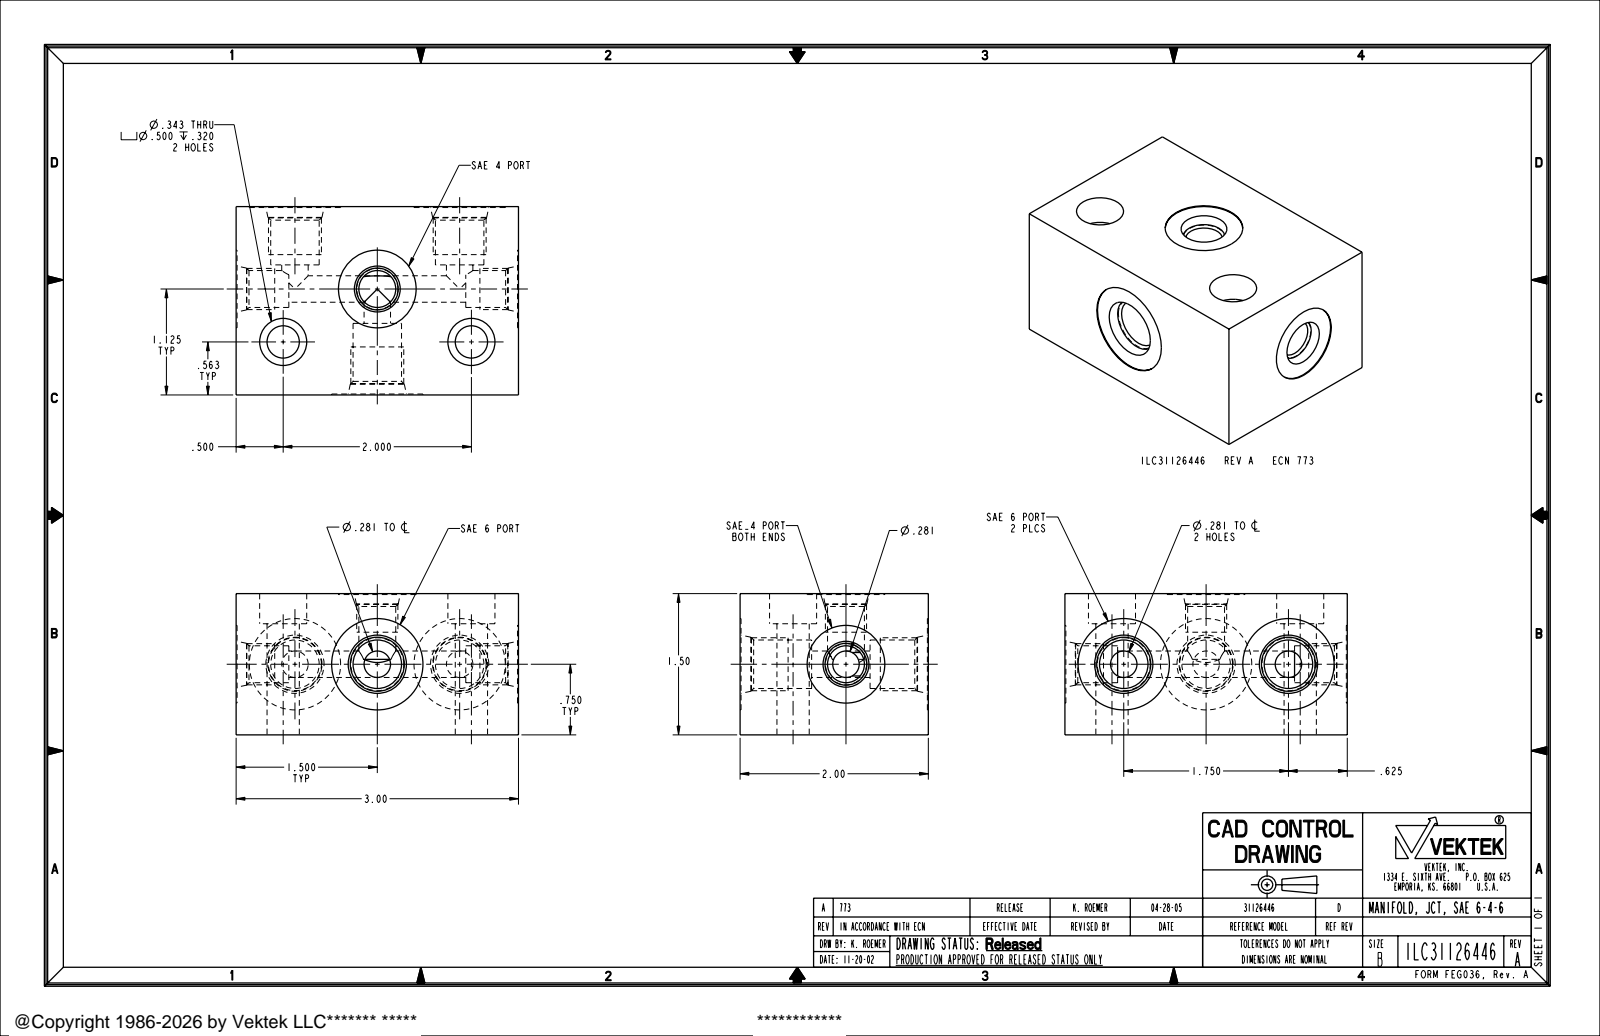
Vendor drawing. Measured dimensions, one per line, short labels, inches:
name: ILC31126446
written by: PRO/ENGINEER BY PARAMETRIC TECHNOLOGY CORPORATION, 2004290 (AUTOMOTIVE_DESIGN_CC2)
unit: in
bodies: 1 solid, 105 faces (25 planar, 53 cylindrical, 27 other)
size: 3 × 2 × 1.5
volume: 7.812 in³; area: 40.34 in²
holes: 4× ⌀0.281, 3× ⌀0.515, 3× ⌀0.97, 2× ⌀0.343, 2× ⌀0.392, 2× ⌀0.5, 2× ⌀0.825
bosses: 3× ⌀0.563, 2× ⌀0.437
face distances: 1.5, 2, 3, 1.99, 2.99, 1.98, 2.98, 1.49, 0.619, 0.609
hole spacings: 0.875, 1.147, 1.75, 2
